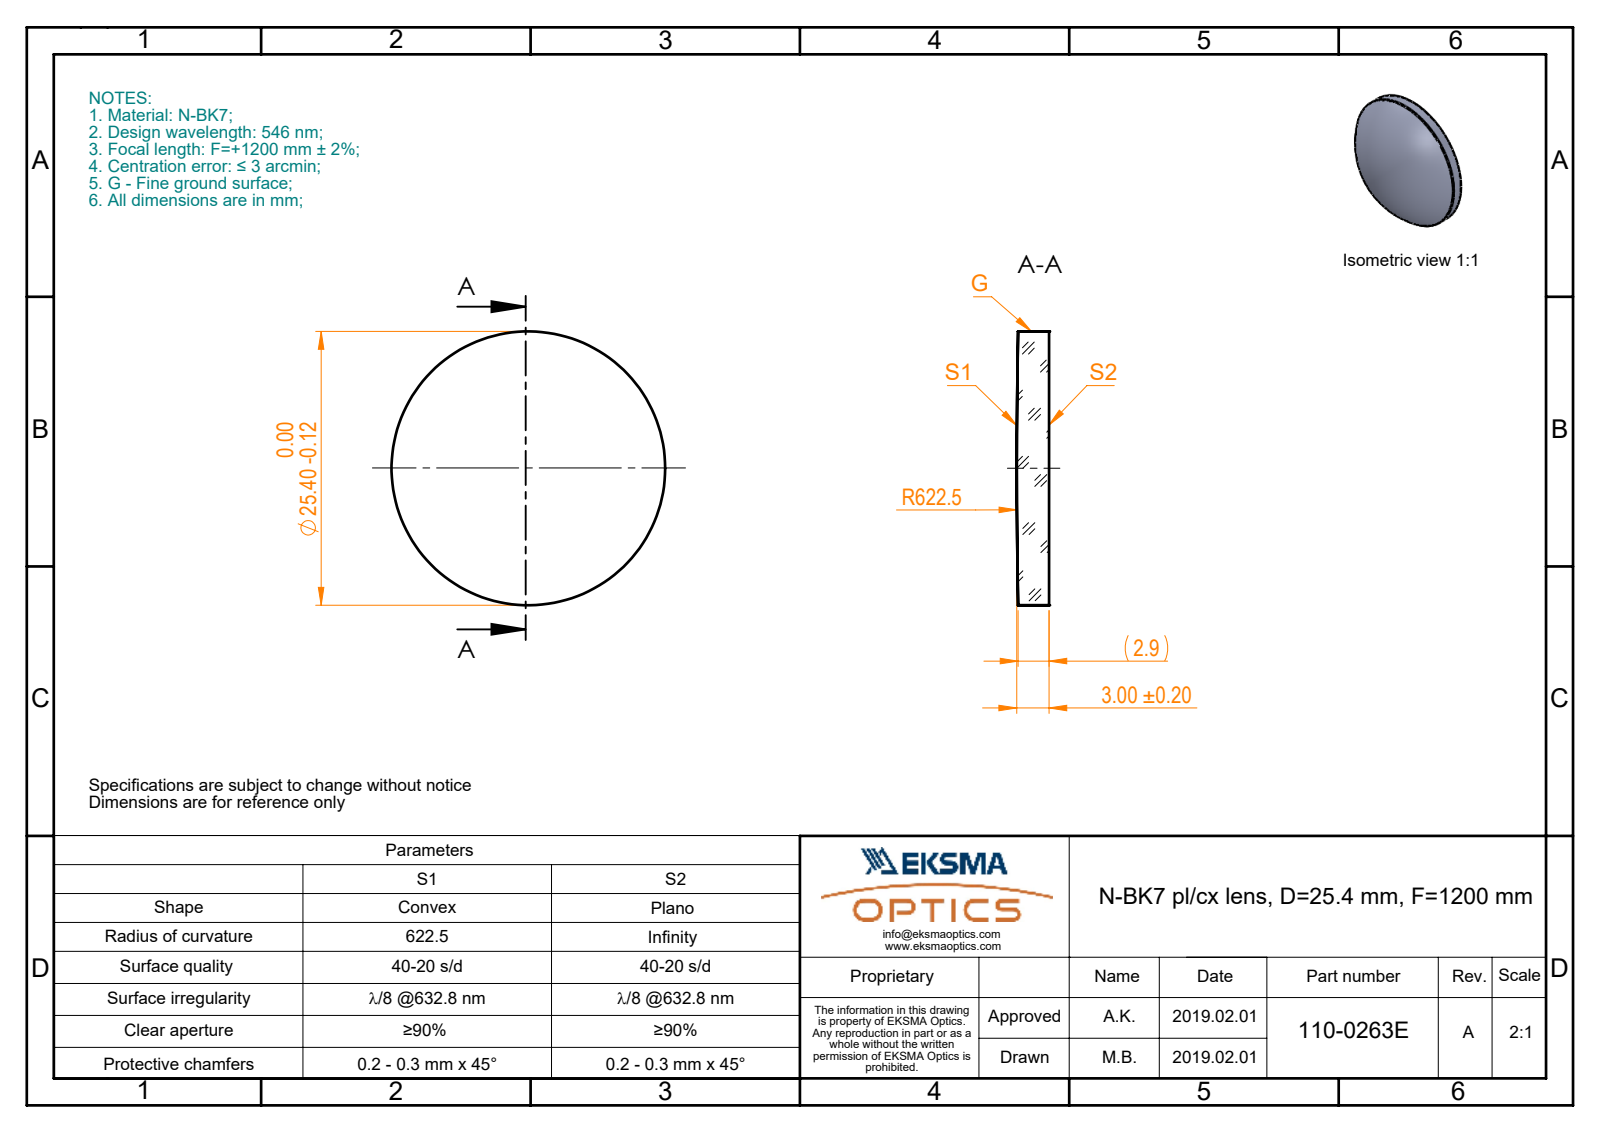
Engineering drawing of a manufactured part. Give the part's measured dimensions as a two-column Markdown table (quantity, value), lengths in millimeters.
| quantity | value |
| --- | --- |
| part name | 110-0263E BK7 pl-cx 25.4 F1200 |
| STEP written by | SolidWorks 2017 (CONFIG_CONTROL_DESIGN) |
| units | millimeters |
| bodies | 1 solid, 5 faces (1 planar, 2 cylindrical, 2 other) |
| overall size | 25.4 × 25.4 × 3 |
| volume | 1 487 mm³ |
| surface area | 1 243 mm² |
| round bosses / shafts (diameter × count) | 25.4 × 1 |
